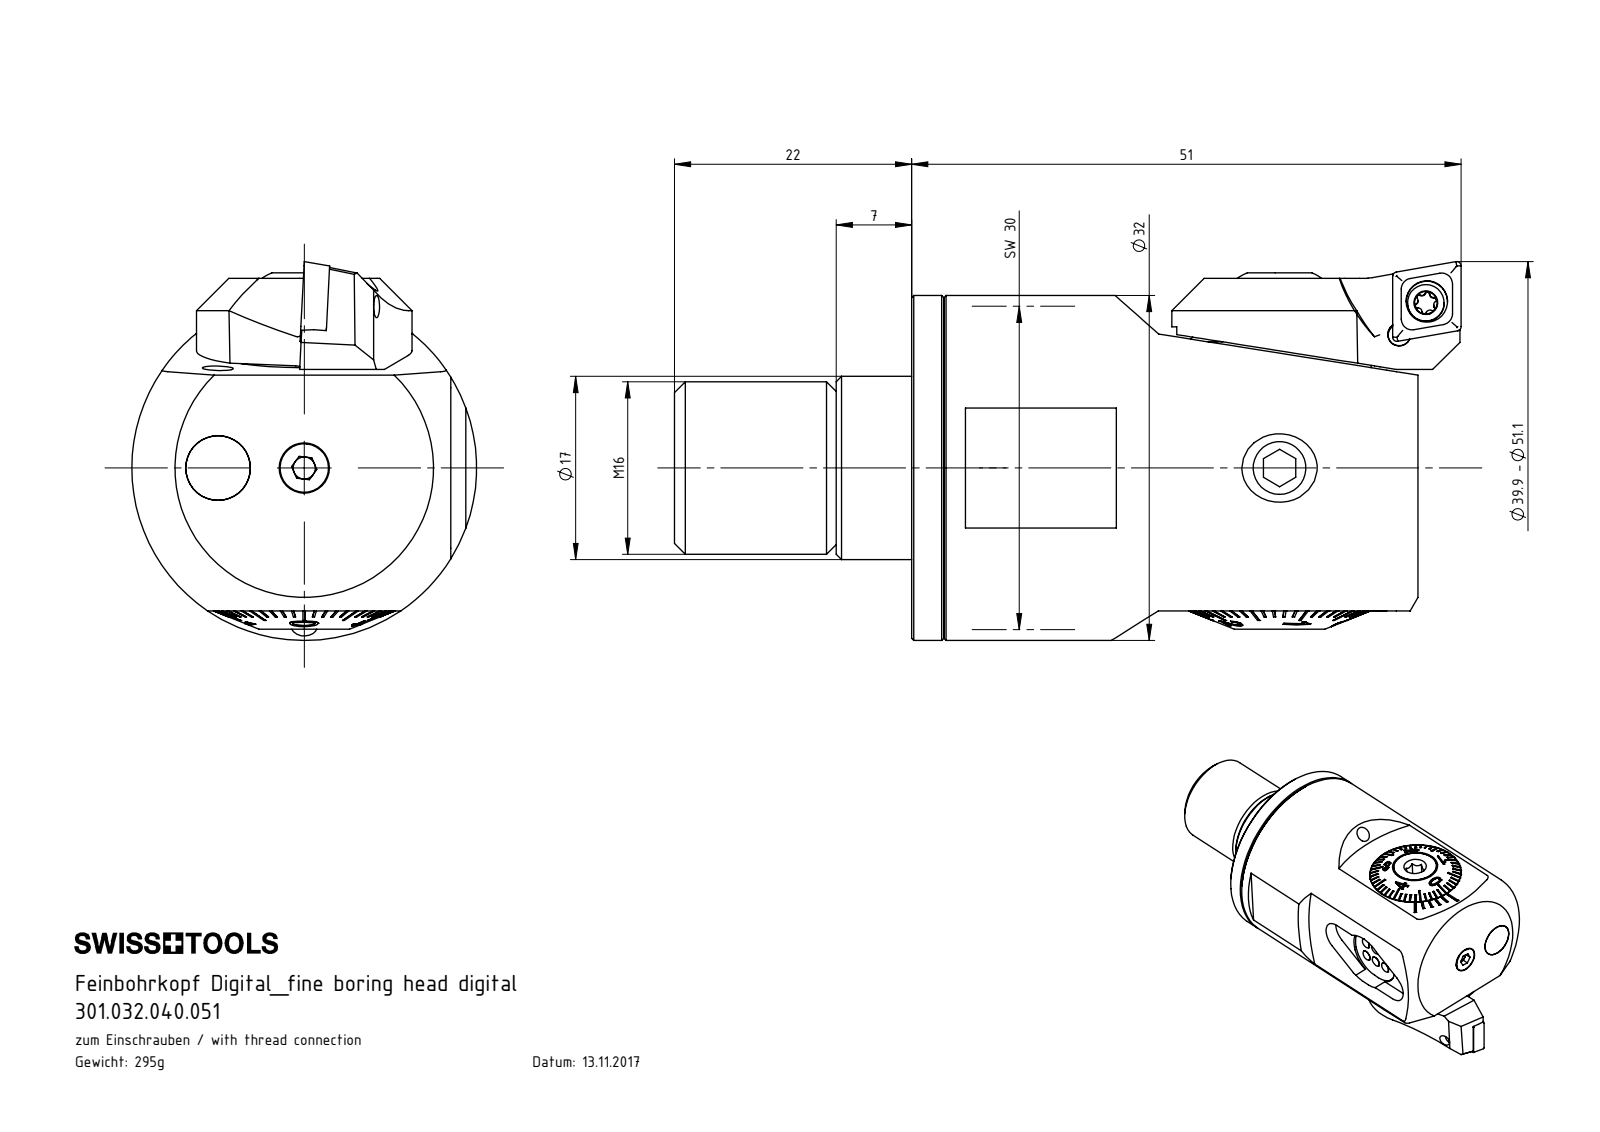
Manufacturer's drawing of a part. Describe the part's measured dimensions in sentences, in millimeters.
The part is named "301.032.040.051; F32-BG1.DA2.017_Aktuell 0.6.2014-Mx1.3; PEE-DA1.011.026_A; Fxx-MAB.xxx.xxx_A_F32x1.3 (+8 more)". Its 3-D file was written by "SolidWorks 2017 (CONFIG_CONTROL_DESIGN)". It is 22 solids with 931 faces: 412 planar, 201 cylindrical and 318 other. Overall it measures 73 by 35.15 by 32 millimeters. Its volume is 37 875 cubic millimeters and its surface area 20 780 square millimeters. Round holes: 5 of diameter 2.5, 2 of diameter 2.05, 2 of diameter 5, 2 of diameter 17, 1 of diameter 0.7, 1 of diameter 2.1, 1 of diameter 2.7, 1 of diameter 2.8, 1 of diameter 2.9, 1 of diameter 3, 1 of diameter 3.3, 1 of diameter 3.85. Round bosses or shafts: 6 of diameter 1.9, 2 of diameter 6, 2 of diameter 2.5, 1 of diameter 32, 1 of diameter 16.98, 1 of diameter 16.85, 1 of diameter 16, 1 of diameter 14.65. Partial cylindrical surfaces (rounded edges, fillets, slot ends): 6 of radius 0.21, 5 of radius 0.36, 4 of radius 0.5, 3 of radius 1.1, 3 of radius 1.2, 2 of radius 1.75, 2 of radius 2.6, 2 of radius 3.1. The main face-to-face distances are 3, 47, 44, 4.5, 25.35, 20.85, 8, 5.5, 1.5, 3.7. The hole center spacings are 2.6, 2.84, 3.84, 3.99, 5.7, 8, 11.68, 25.15.
